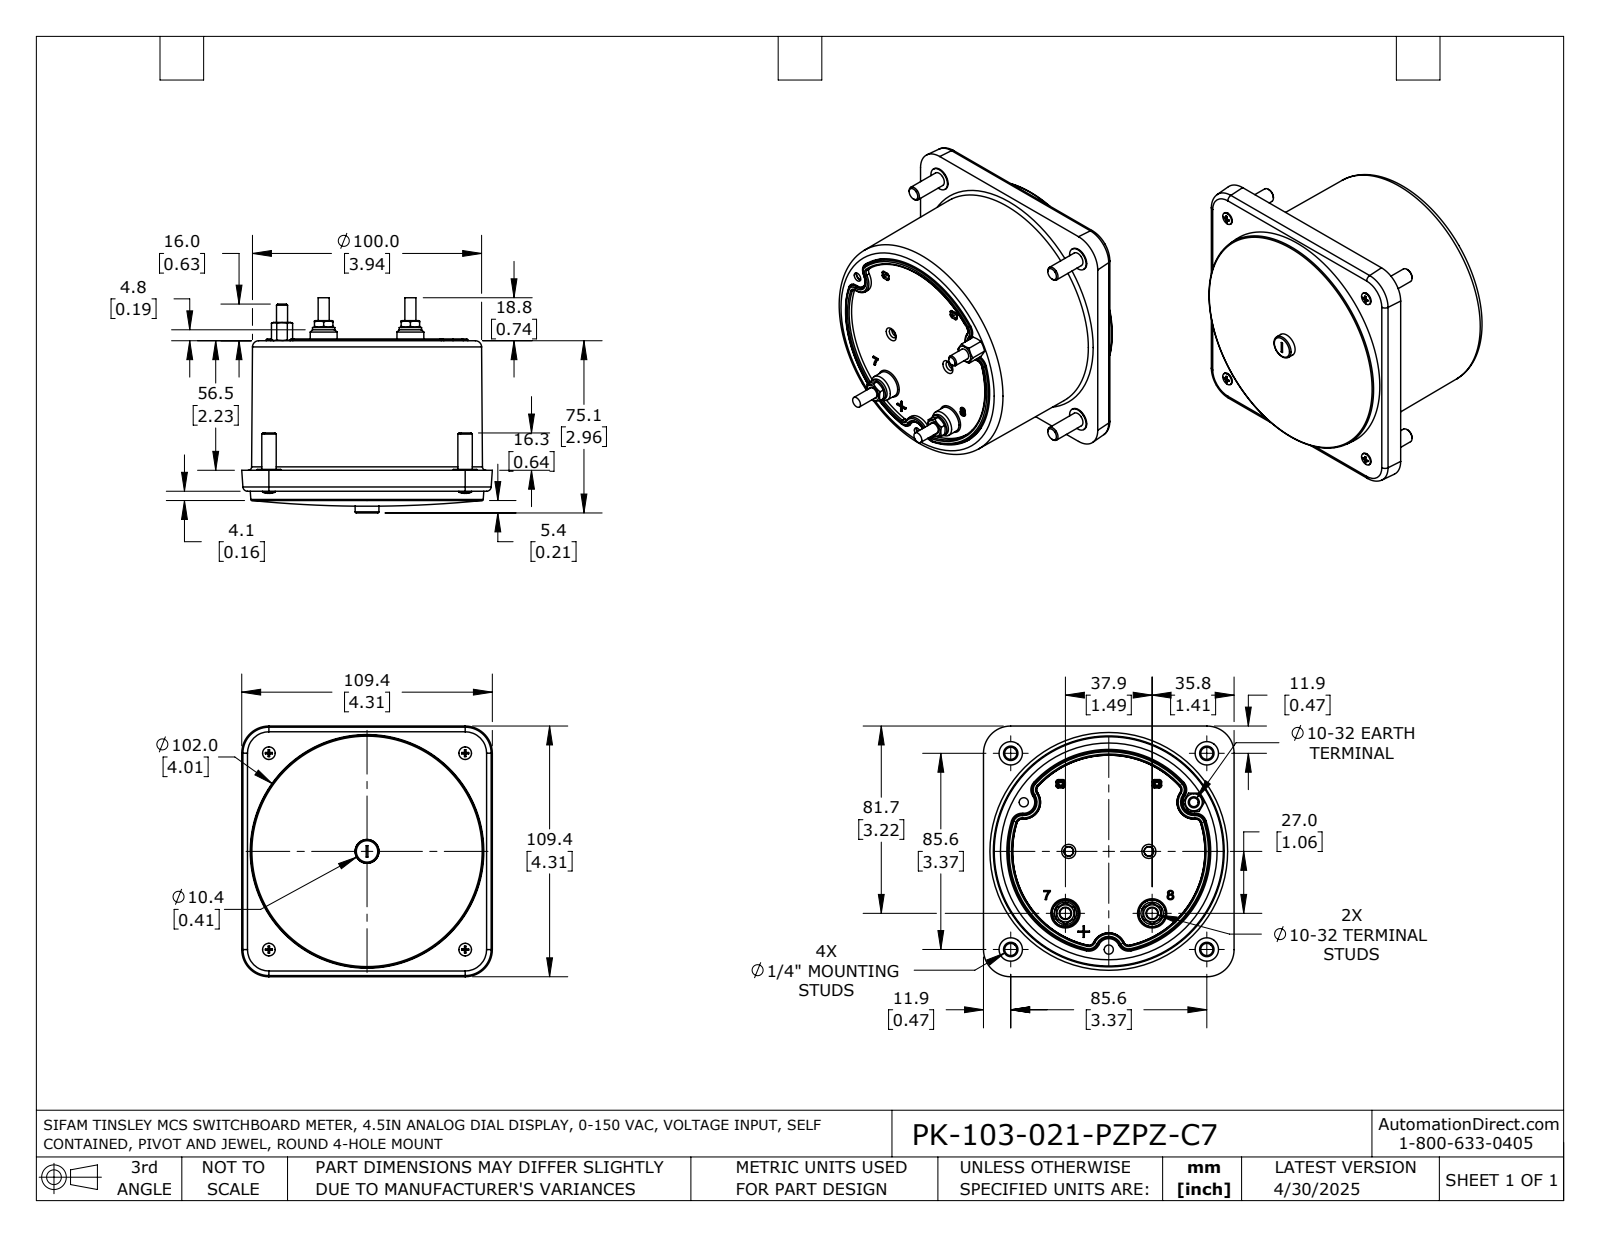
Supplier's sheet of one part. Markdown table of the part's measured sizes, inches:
| quantity | value |
| --- | --- |
| part name | PK-103-021-PZPZ-C7 |
| STEP written by | SolidWorks 2021 (AUTOMOTIVE_DESIGN) |
| units | inches |
| bodies | 1 solid, 609 faces (167 planar, 141 cylindrical, 301 other) |
| overall size | 4.307 × 4.307 × 3.697 |
| volume | 36.28 in³ |
| surface area | 82.21 in² |
| round holes (diameter × count) | 0.094 × 4, 0.138 × 4, 0.315 × 4, 0.157 × 3, 0.209 × 2 |
| round bosses / shafts (diameter × count) | 0.402 × 4, 0.248 × 4, 0.217 × 4, 0.114 × 4, 0.19 × 3, 0.384 × 2, 0.146 × 1 |
| partial cylindrical surfaces (radius × count) | 0.02 × 24, 0.189 × 9, 0.079 × 4, 1.752 × 1 |
| main face-to-face distances | 2.177, 2.537, 0.36, 0.048, 2.225, 2.585, 0.489, 2.715, 2.667, 0.129 |
| hole center spacings | 3.372, 3.37, 3.374, 3.378, 3.38, 4.769, 0.971, 1.126 |
